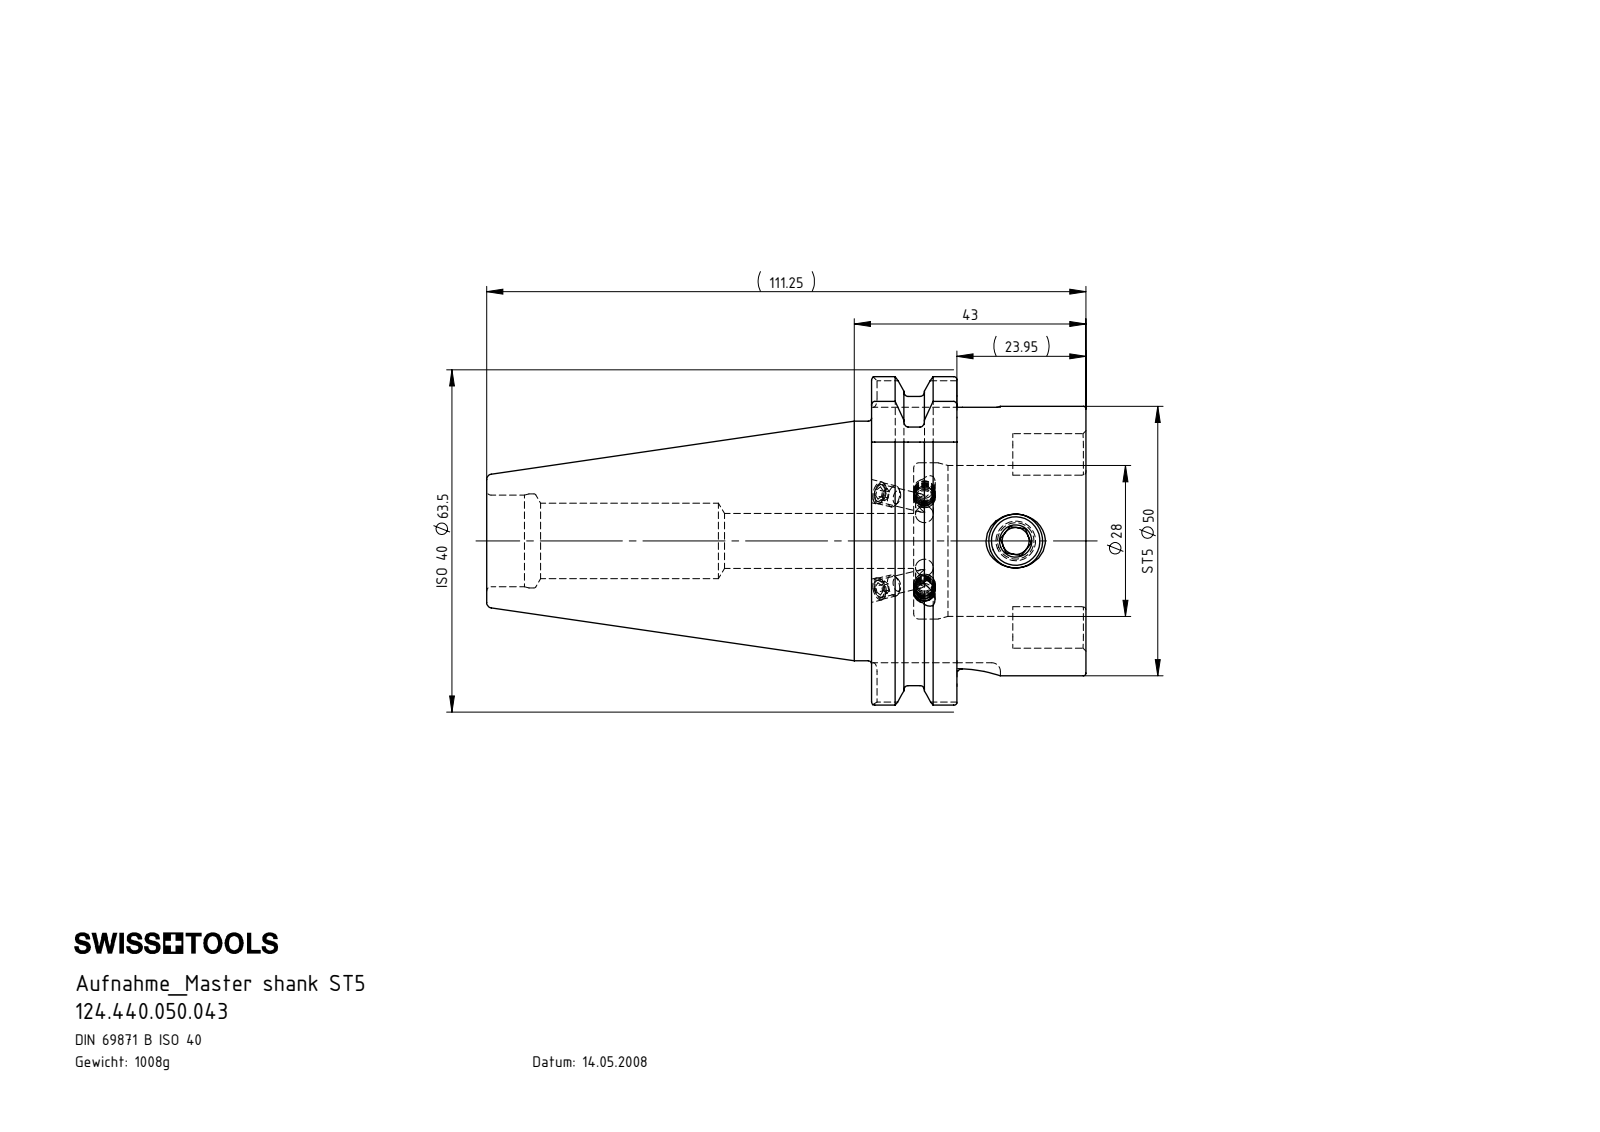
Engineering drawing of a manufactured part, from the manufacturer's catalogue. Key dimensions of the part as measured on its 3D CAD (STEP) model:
Part name (STEP PRODUCT): SB4.ST5.K01.043; ST5-ER1.001.012_A; SB4-ST5.K01.043_B_mit Bundkhlung; KVT_MB_600_040 (+1 more)
STEP written by: SolidWorks 2017 (AUTOMOTIVE_DESIGN)
Units: millimetres
Bodies: 8 solids, 212 faces (80 planar, 52 cylindrical, 80 other)
Overall size (bounding box): 111.25 × 63.5 × 60.94
Volume: 128 388 mm³ · Surface area: 27 892 mm²
Round holes (diameter × count): ⌀3.3 ×3, ⌀3 ×2, ⌀4.2 ×2, ⌀4 ×1, ⌀5 ×1, ⌀9 ×1, ⌀10.2 ×1, ⌀14 ×1, ⌀17 ×1, ⌀17.45 ×1, ⌀28 ×1, ⌀29 ×1
Round bosses / shafts (diameter × count): ⌀4 ×4, ⌀50 ×1, ⌀44.45 ×1, ⌀10 ×1
Partial cylindrical surfaces — rounded edges, fillets, slot ends (radius × count): R1.6 ×8, R4.2 ×2, R8.05 ×1, R28 ×1, R31.75 ×1
Main face-to-face distances: 39.8, 15.85, 23.95, 7.8, 8.05, 32, 47.4, 24.1, 71.45, 79.25
